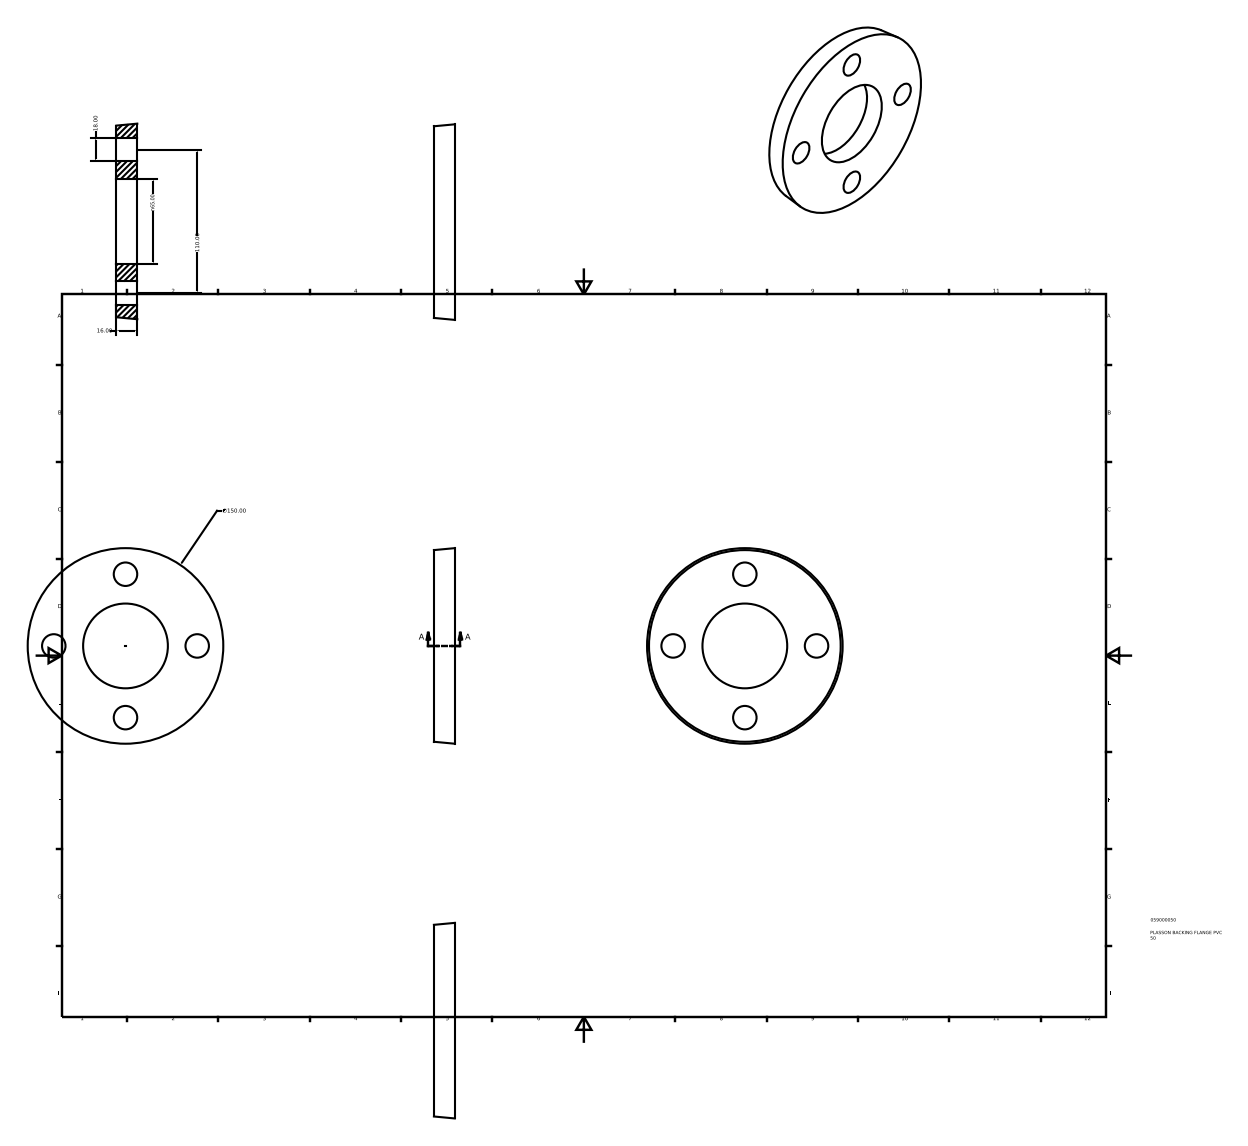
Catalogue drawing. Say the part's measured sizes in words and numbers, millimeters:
The part is named "059000050". Its 3-D file was written by "Autodesk Inventor 2015 (AUTOMOTIVE_DESIGN)". It is 1 solid with 8 faces: 2 planar, 5 cylindrical and 1 other. Overall it measures 150 by 150 by 16 millimeters. Its volume is 207 747 cubic millimeters and its surface area 40 354 square millimeters. Round holes: 4 of diameter 18, 1 of diameter 65. The main face-to-face distances are 16. The hole center spacings are 55, 77.78, 110.
